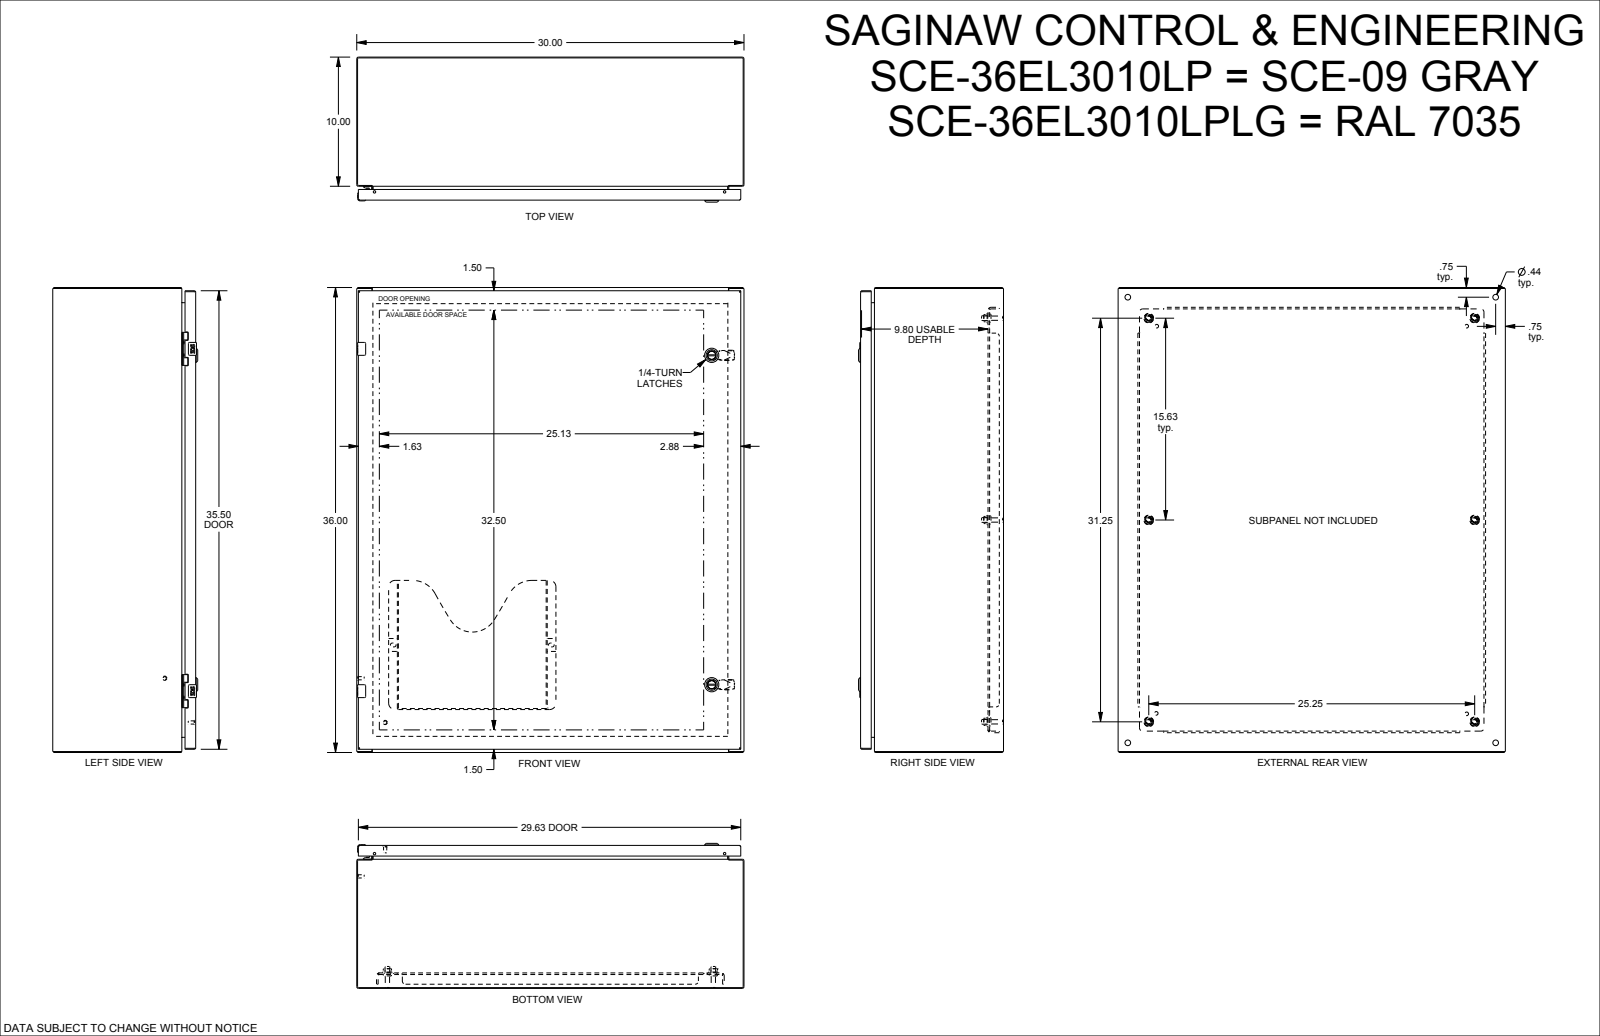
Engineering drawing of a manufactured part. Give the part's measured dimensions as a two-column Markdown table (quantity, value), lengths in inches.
| quantity | value |
| --- | --- |
| part name | SCE-36EL3010LP |
| STEP written by | SolidWorks 2021 (AUTOMOTIVE_DESIGN) |
| units | inches |
| bodies | 49 solids, 2509 faces (993 planar, 866 cylindrical, 650 other) |
| overall size | 36 × 30 × 11.23 |
| volume | 427.2 in³ |
| surface area | 10 120 in² |
| round holes (diameter × count) | 0.367 × 6, 0.5 × 6, 0.172 × 4, 0.205 × 4, 0.244 × 4, 0.266 × 4, 0.281 × 4, 0.375 × 4, 0.437 × 4, 0.04 × 2, 0.188 × 2, 0.197 × 2 |
| round bosses / shafts (diameter × count) | 0.366 × 6, 0.332 × 6, 0.17 × 6, 0.25 × 4, 0.248 × 4, 0.24 × 4, 0.196 × 3, 1.102 × 2 |
| partial cylindrical surfaces (radius × count) | 0.012 × 56, 0.01 × 40, 0.015 × 20, 0.02 × 20, 0.04 × 17, 0.06 × 13, 0.1 × 12, 0.031 × 10 |
| main face-to-face distances | 0.075, 0.06, 11.083, 11.008, 11.024, 10.948, 1.2, 1.125, 9.824, 9.883 |
| hole center spacings | 15.625, 0.985, 17.326, 26.5, 32.915, 42.462, 15.019, 30.638 |
